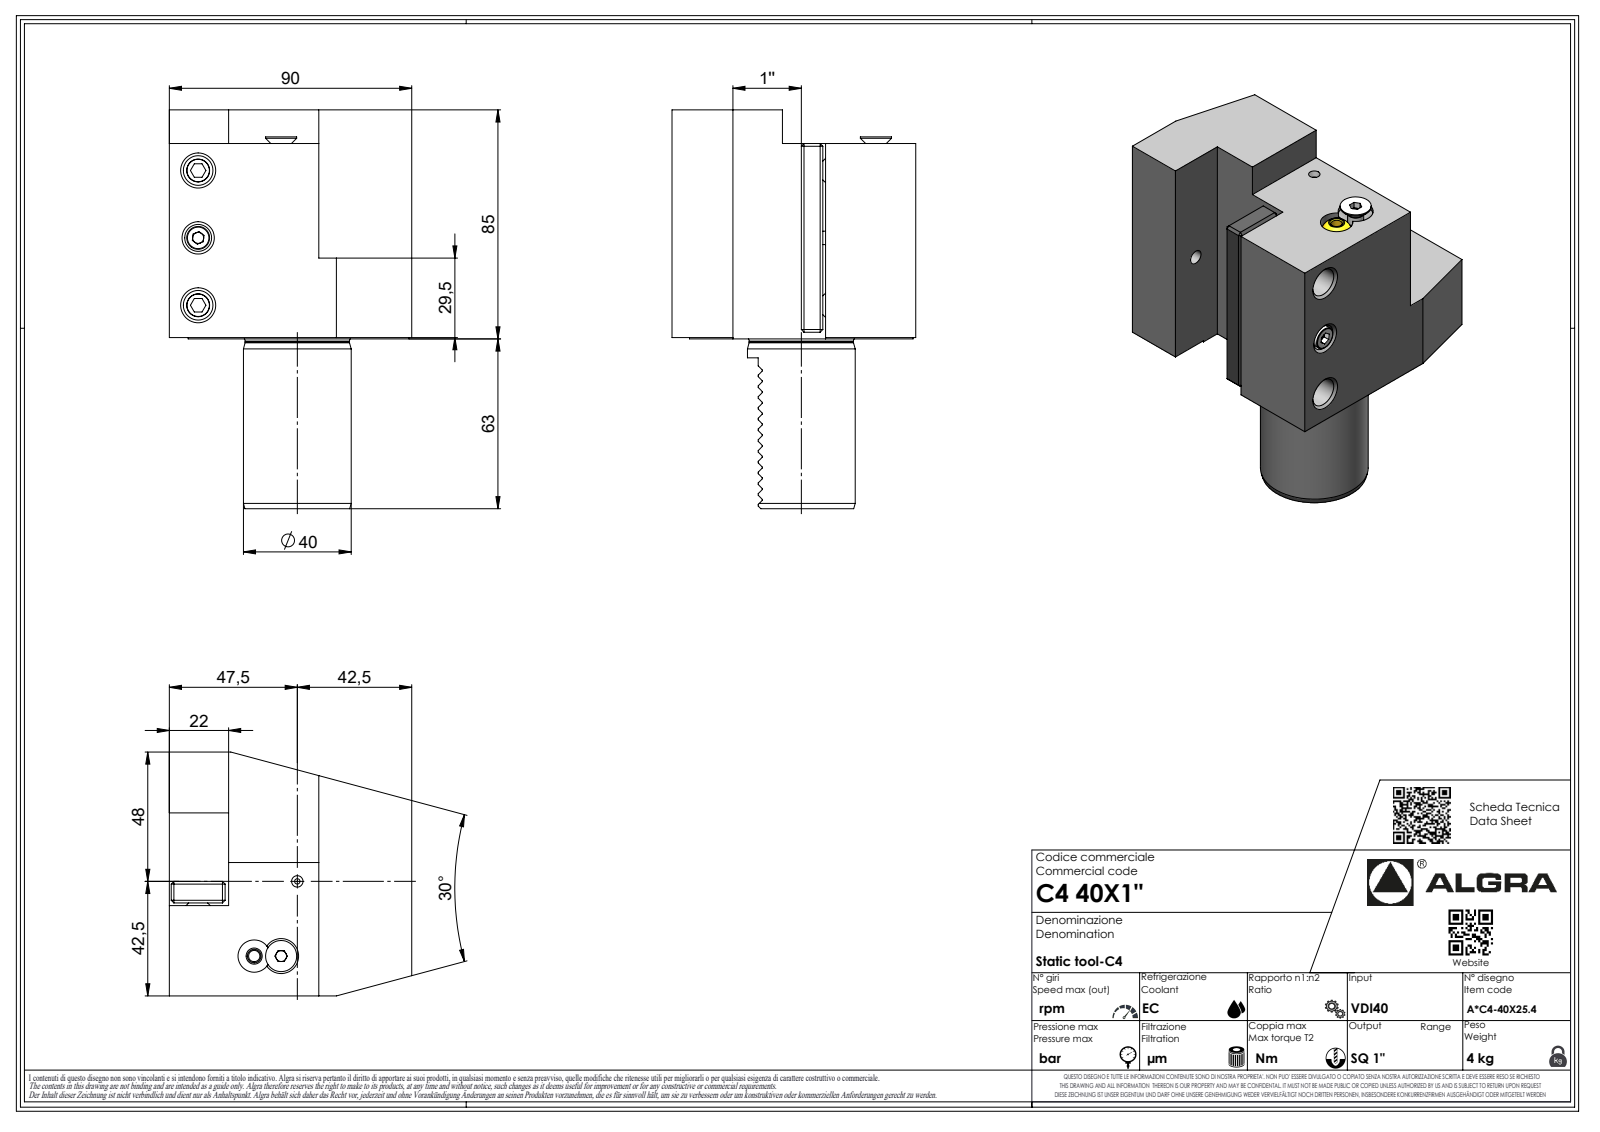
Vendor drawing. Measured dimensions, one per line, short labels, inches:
name: C440X1
written by: SolidWorks 2023 (AUTOMOTIVE_DESIGN)
unit: in
bodies: 1 solid, 314 faces (243 planar, 43 cylindrical, 28 other)
size: 5.827 × 3.563 × 3.543
volume: 29.46 in³; area: 79.26 in²
holes: 1× ⌀0.083
bosses: 1× ⌀1.575, 1× ⌀1.524, 1× ⌀0.251, 1× ⌀0.067
rounds: 13× R0.012, 7× R0.013, 7× R0.02, 7× R0.146, 1× R0.008, 1× R1.634
face distances: 2.185, 1.673, 1.319, 0.866, 1.181, 2.854, 3.543, 2.677, 3.563, 1.358
